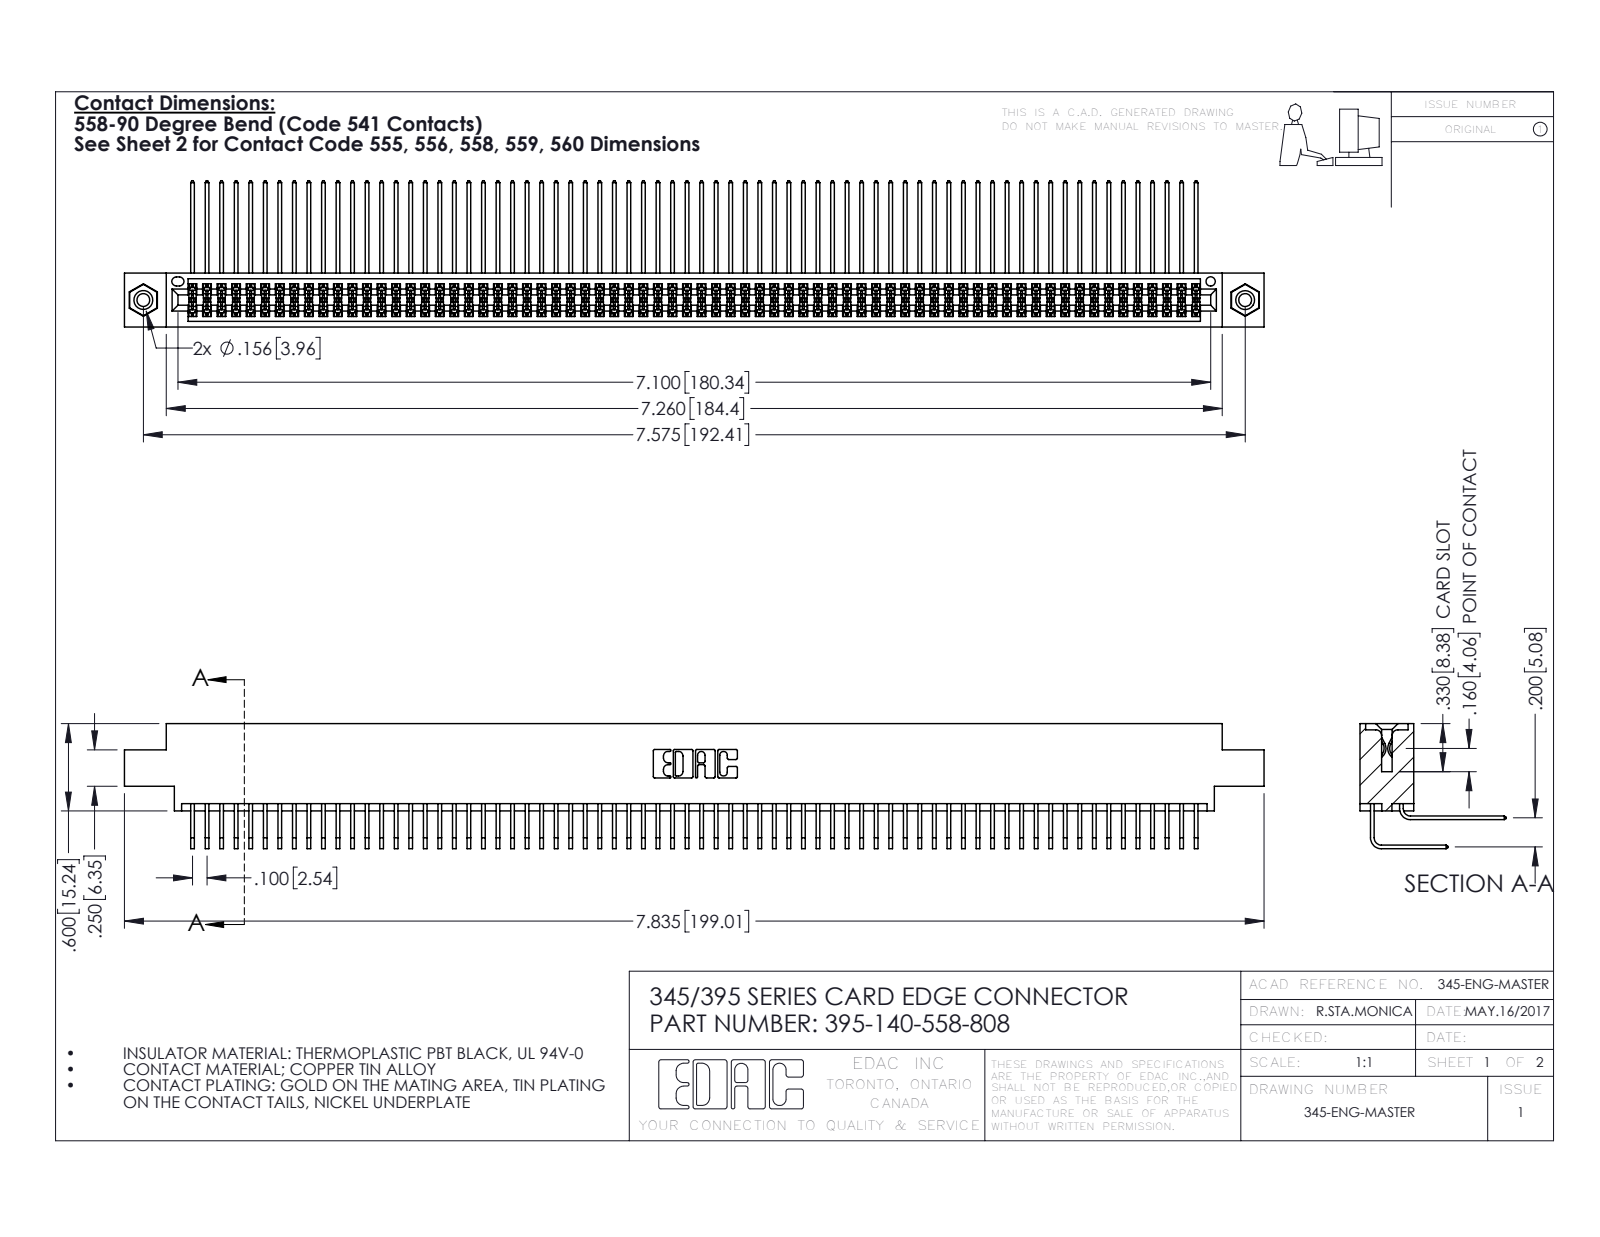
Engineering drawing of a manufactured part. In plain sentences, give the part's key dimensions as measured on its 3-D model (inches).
The part is named "345 Part_0.170 Offset - 0.156 Dia-TI; 395-140-558-808; 345-250-001_345-250-003-102; 345-292-001_558 Tail - 2 (+1 more)". Its 3-D file was written by "SolidWorks 2016 (CONFIG_CONTROL_DESIGN)". It is 143 solids with 7470 faces: 5016 planar, 2438 cylindrical and 16 other. Overall it measures 7.835 by 1.005 by 0.859 inches. Its volume is 1.238 cubic inches and its surface area 53.43 square inches. Round holes: 2 of diameter 0.089, 2 of diameter 0.125, 2 of diameter 0.156, 1 of diameter 0.064. Round bosses or shafts: 2 of diameter 0.155. Partial cylindrical surfaces (rounded edges, fillets, slot ends): 279 of radius 0.006, 22 of radius 0.01, 6 of radius 0.007, 6 of radius 0.031, 3 of radius 0.026, 2 of radius 0.014, 2 of radius 0.019, 2 of radius 0.022. The main face-to-face distances are 0.072, 0.298, 0.2, 0.37, 0.098, 0.272, 0.025, 0.225, 0.175, 0.025. The hole center spacings are 0.27, 7.339, 7.575.
